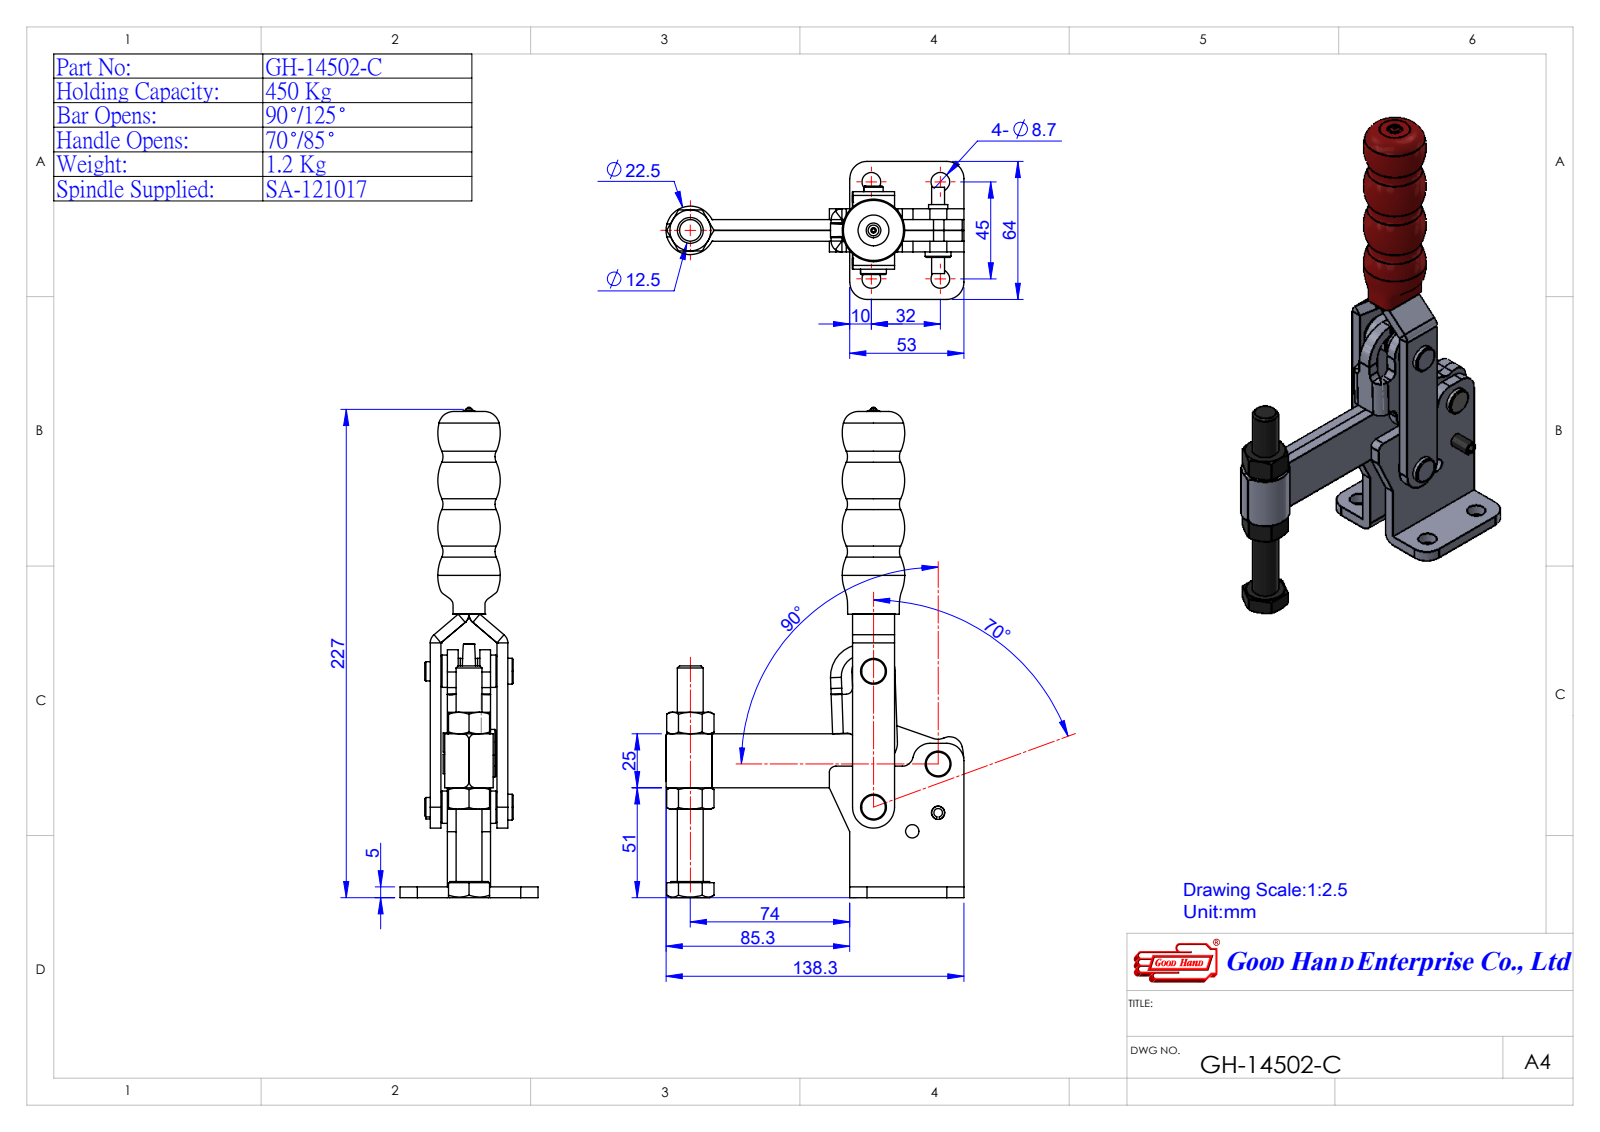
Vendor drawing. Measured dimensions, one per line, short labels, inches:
name: Group2^GH-14502-C(簡化); Group6^GH-14502-C(簡化); Group1^GH-14502-C(簡化); GH-14502-C(簡化) (+2 more)
written by: SolidWorks 2016 (AUTOMOTIVE_DESIGN)
unit: in
bodies: 5 solids, 598 faces (256 planar, 147 cylindrical, 195 other)
size: 8.957 × 5.443 × 2.52
volume: 11.62 in³; area: 107.1 in²
holes: 4× ⌀0.276, 4× ⌀0.343, 1× ⌀0.075, 1× ⌀0.236, 1× ⌀0.402, 1× ⌀0.472, 1× ⌀0.492
bosses: 4× ⌀0.394, 2× ⌀0.512, 2× ⌀0.354, 2× ⌀0.352, 1× ⌀0.886, 1× ⌀0.709, 1× ⌀0.244, 1× ⌀0.072
rounds: 8× R0.197, 5× R0.315, 3× R0.029, 3× R0.03, 2× R0.118, 2× R0.236, 2× R0.394, 1× R0.032
face distances: 0.197, 0.591, 0.394, 0.315, 0.906, 0.787, 0.512, 1.102, 0.118, 1.22
hole spacings: 1.26, 1.772, 2.174, 3.424, 4.652, 0.835, 1.183, 1.202
